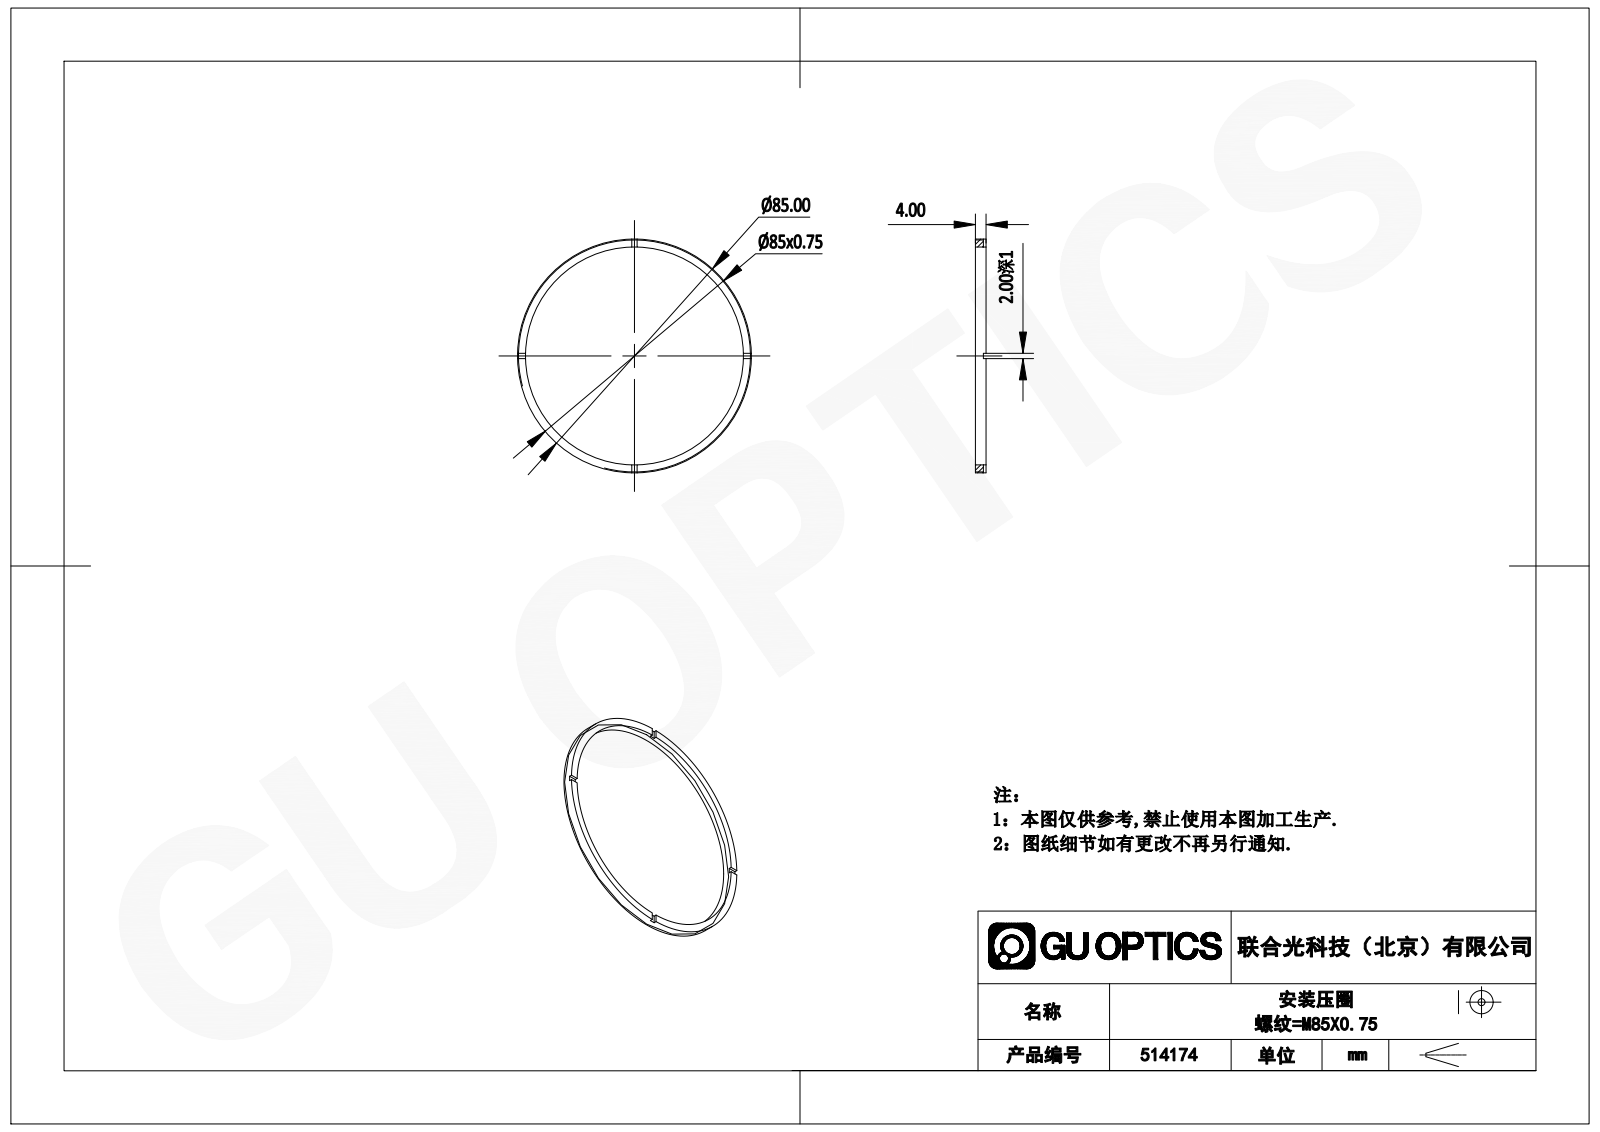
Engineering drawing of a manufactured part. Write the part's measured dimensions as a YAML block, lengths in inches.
part_name: "514174"
step_written_by: "SolidWorks 2020 (CONFIG_CONTROL_DESIGN)"
units: inches
bodies: {solids: 1, faces: 21, planar: 17, cylindrical: 4, other: 0}
overall_size: [3.346, 3.346, 0.157]
volume: 0.187
surface_area: 5.603
round_holes:
  - {diameter: 3.11, count: 1}
round_bosses_or_shafts:
  - {diameter: 3.346, count: 1}
face_to_face_distances: [0.157, 0.118, 0.039, 0.079]
